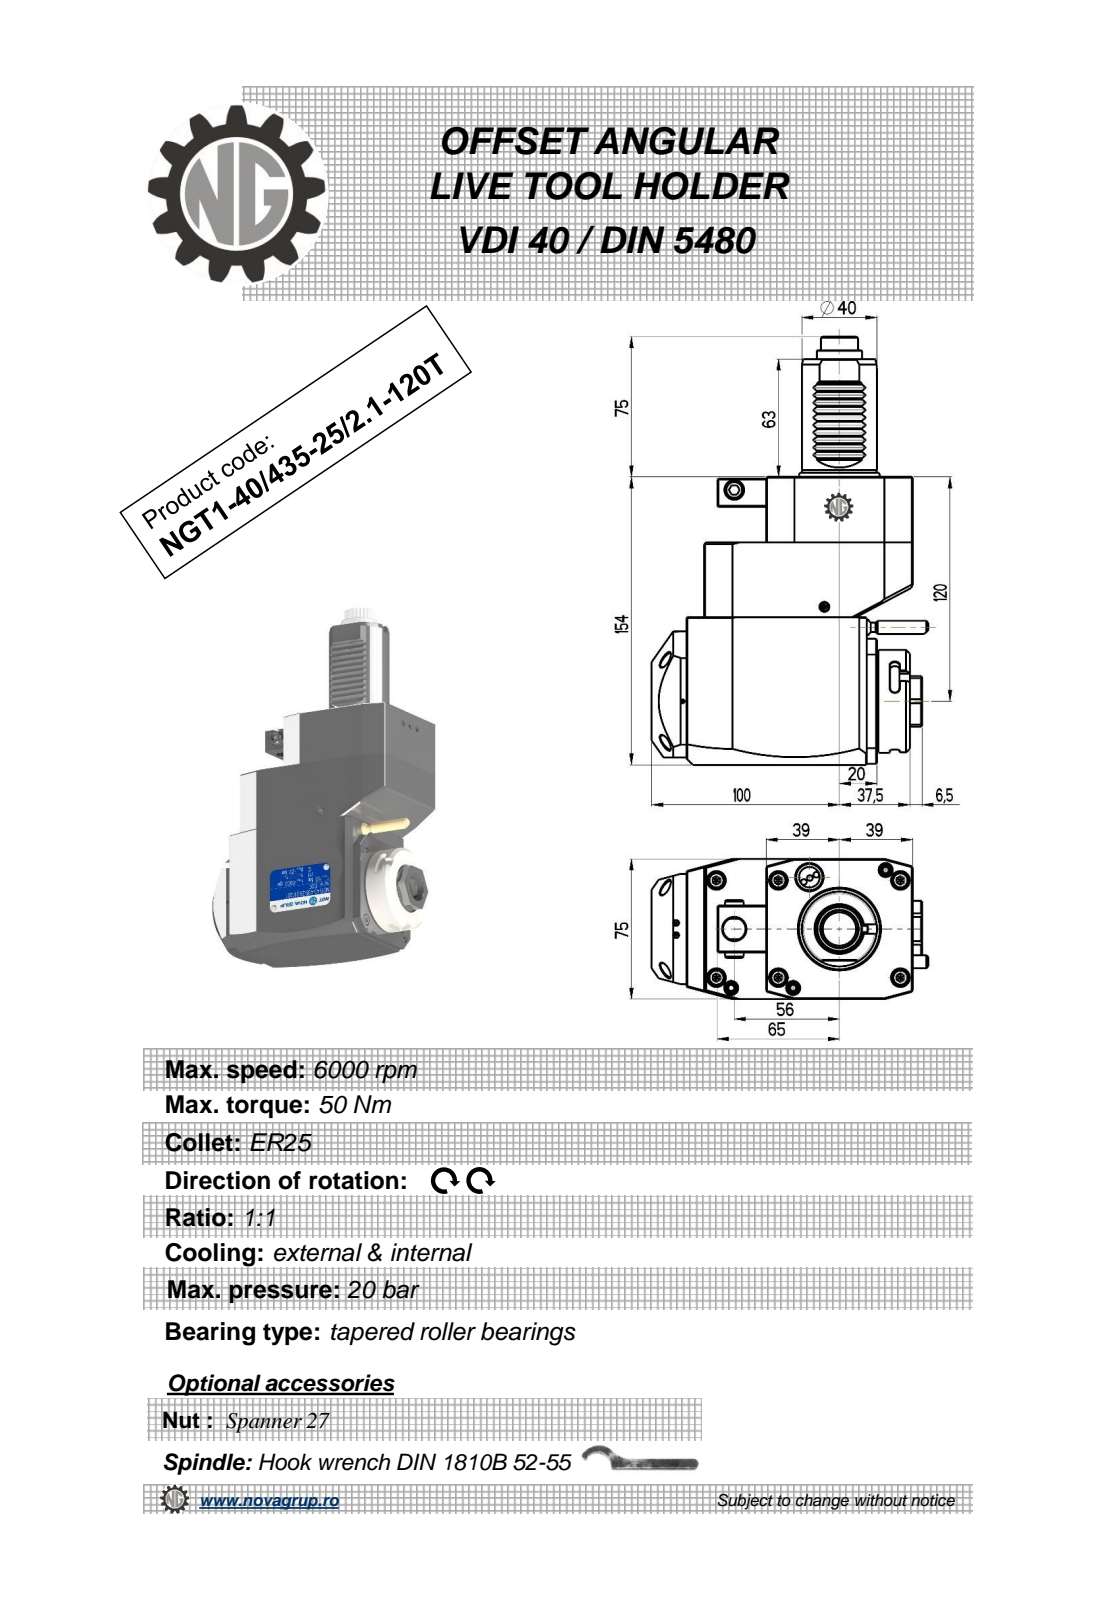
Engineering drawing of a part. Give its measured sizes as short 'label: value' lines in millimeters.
name: NGT1_40_435_25_1_1_120T
written by: PRO/ENGINEER BY PARAMETRIC TECHNOLOGY CORPORATION, 2010280 (CONFIG_CONTROL_DESIGN)
unit: mm
bodies: 1 solid, 449 faces (189 planar, 166 cylindrical, 94 other)
size: 229 × 147.33 × 75
volume: 1 270 000 mm³; area: 88 598 mm²
holes: 1× ⌀2.5, 1× ⌀3, 1× ⌀8.5, 1× ⌀9.5, 1× ⌀12, 1× ⌀18
bosses: 2× ⌀8.96, 1× ⌀55, 1× ⌀48, 1× ⌀40, 1× ⌀24, 1× ⌀10, 1× ⌀7, 1× ⌀5
rounds: 48× R2.08, 10× R0.3, 6× R2.5, 2× R15, 2× R180, 1× R9.08, 1× R9.92, 1× R24.5
face distances: 75, 154, 119, 19, 35, 111, 92, 59, 33, 78
hole spacings: 43.2, 74.1, 111.5
